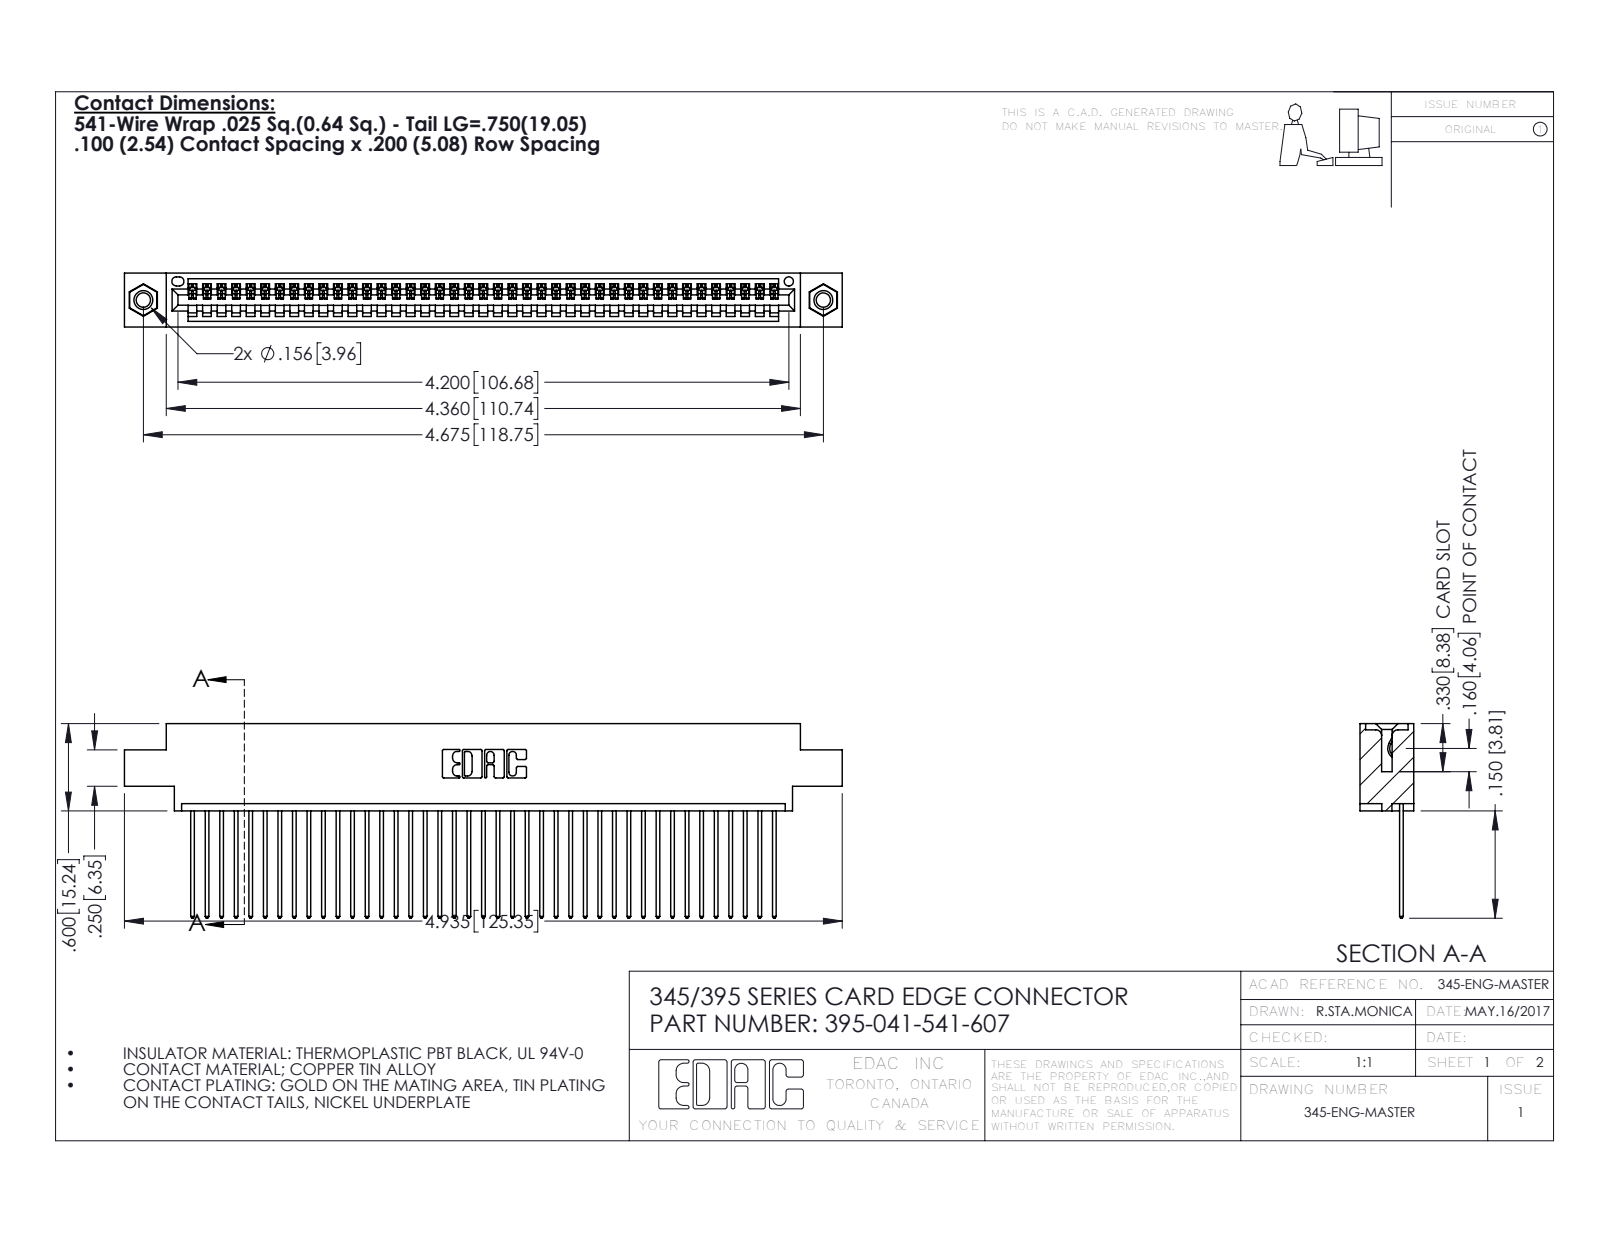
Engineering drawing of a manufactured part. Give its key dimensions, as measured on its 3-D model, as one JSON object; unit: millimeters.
{"part_name": "345-292-001_345-293-141; 395-041-541-607; 345-250-001_345-250-005-103; 345 Part_0.170 Offset - 0.156 Dia-TI", "step_written_by": "SolidWorks 2016 (CONFIG_CONTROL_DESIGN)", "units": "millimeters", "bodies": {"solids": 44, "faces": 2568, "planar": 1756, "cylindrical": 796, "other": 16}, "overall_size": [125.3, 34, 9.4], "volume_mm3": 11900, "surface_area_mm2": 16760, "round_holes": [[2.5, 2], [3.2, 2], [4, 2], [1.6, 1]], "round_bosses_or_shafts": [[3.9, 2]], "partial_cylinders_radius": [[0.2, 82], [0.3, 82], [0.3, 22], [0.2, 6], [0.8, 6], [0.7, 3], [0.8, 2], [1, 2]], "face_to_face_distances": [1.8, 7.6, 9.4, 2.5, 6.9, 0.6, 5.1, 5.7, 4.4, 3.8], "hole_center_spacings": [6.9, 112.8, 118.7]}
